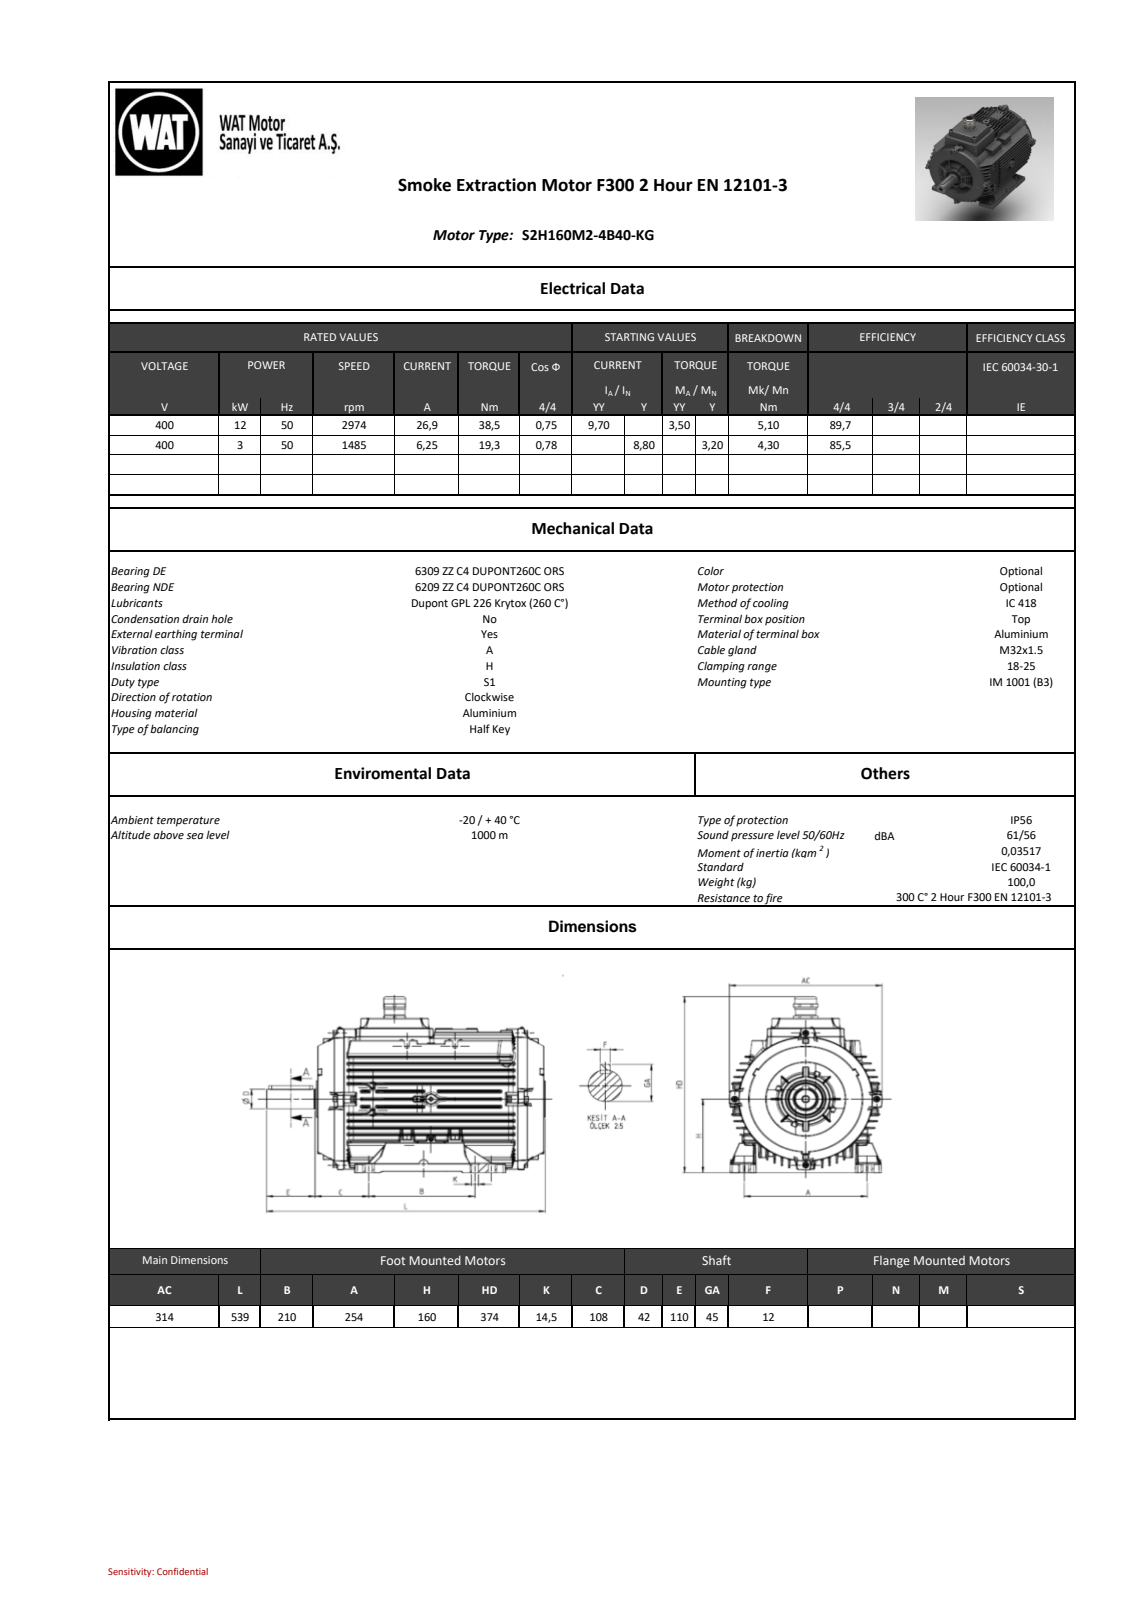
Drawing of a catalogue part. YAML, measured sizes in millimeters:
part_name: "26036A749124ezia"
step_written_by: "SIEMENS PLM Software NX 11.0 (AP203_CONFIGURATION_CONTROLLED_3D_DESIGN_OF_MECHANICAL_PARTS_AND_ASSEMBLIES_MIM_LF)"
units: millimeters
bodies: {solids: 0, faces: 8266, planar: 1766, cylindrical: 2938, other: 3562}
overall_size: [538.5, 373.95, 314]
round_holes:
  - {diameter: 10.2, count: 1}
  - {diameter: 13, count: 1}
  - {diameter: 18, count: 1}
  - {diameter: 54, count: 1}
  - {diameter: 68.67, count: 1}
round_bosses_or_shafts:
  - {diameter: 14.8, count: 4}
  - {diameter: 13, count: 4}
  - {diameter: 10, count: 4}
  - {diameter: 272.5, count: 1}
  - {diameter: 72, count: 1}
  - {diameter: 45, count: 1}
  - {diameter: 42, count: 1}
  - {diameter: 41.4, count: 1}
partial_cylinders:
  - {radius: 1, count: 782}
  - {radius: 0.5, count: 762}
  - {radius: 4, count: 107}
  - {radius: 5, count: 77}
  - {radius: 2.5, count: 50}
  - {radius: 3, count: 13}
  - {radius: 5.5, count: 8}
  - {radius: 9, count: 8}
face_to_face_distances: [11.85, 165.47, 9.32, 168, 2.53, 156.15, 144, 11.92, 21.47, 155.85]
